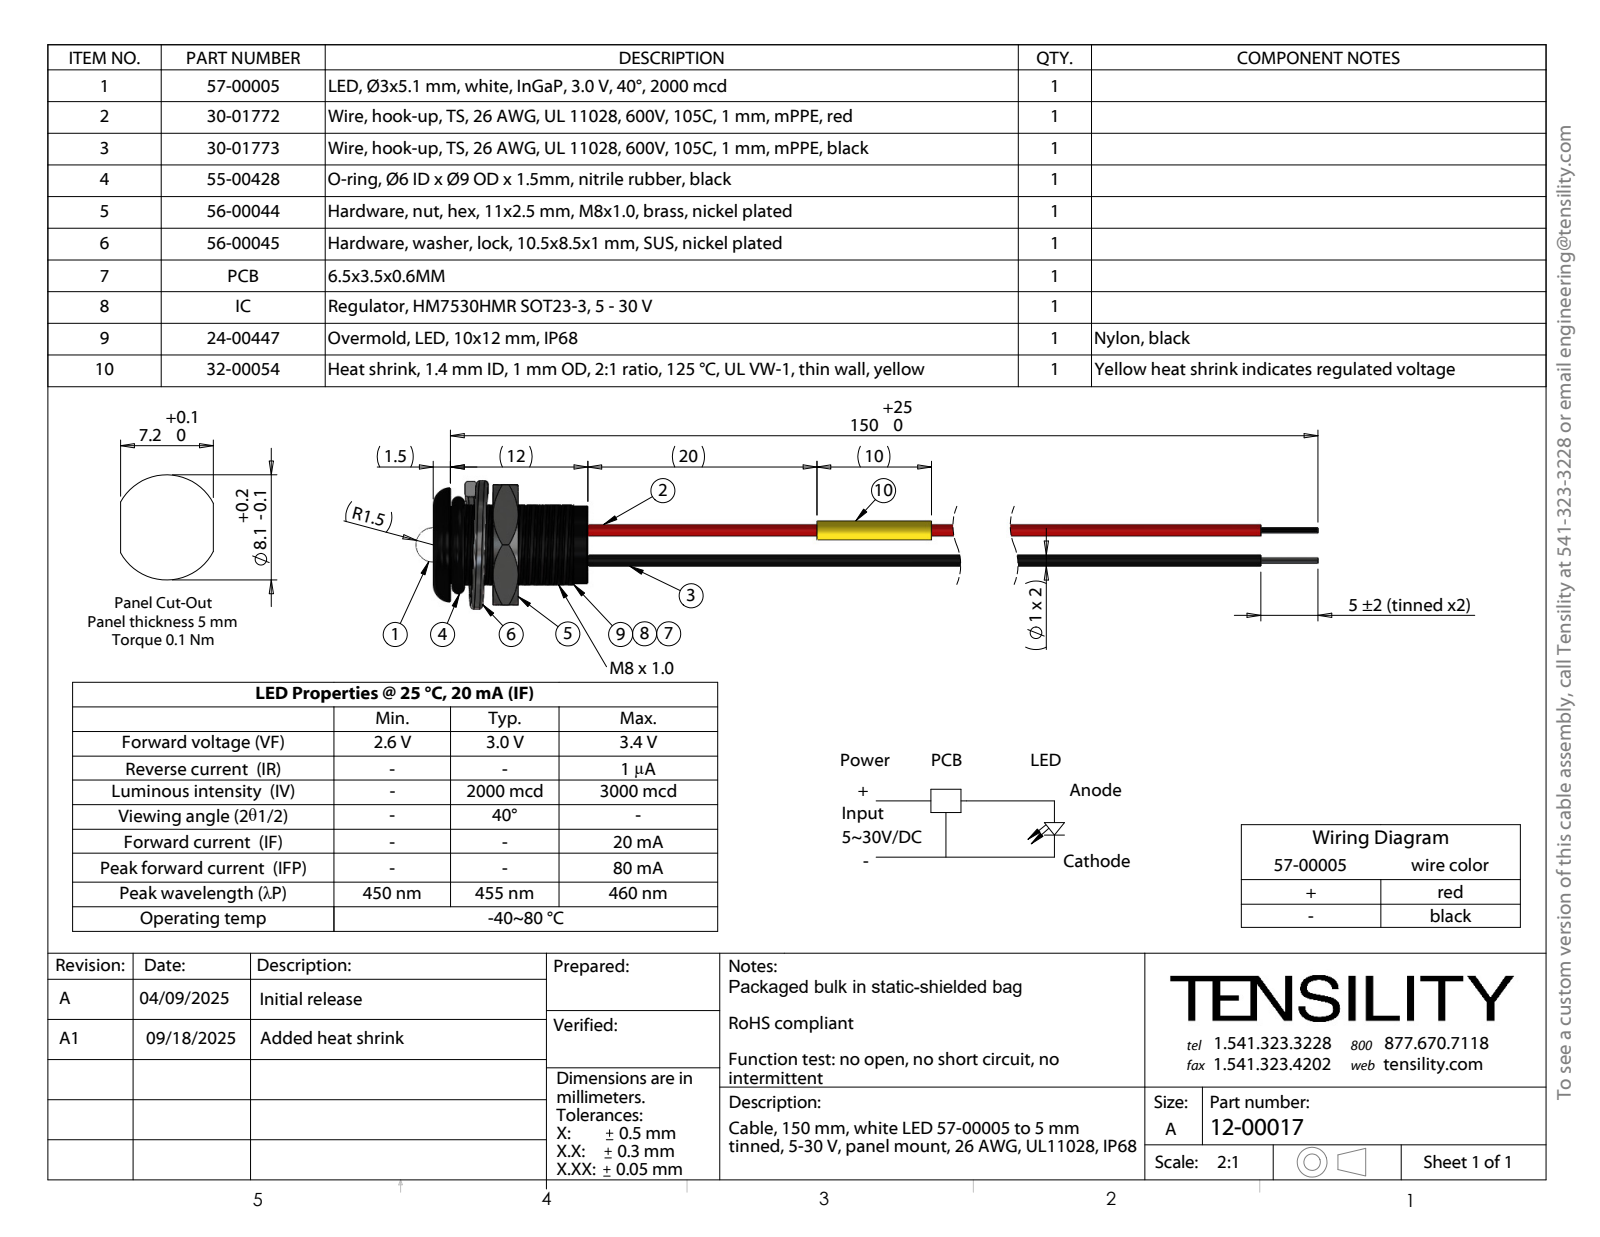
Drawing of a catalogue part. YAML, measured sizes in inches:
part_name: "30-01772_stripped and tinned; 30-01773_stripped and tinned; 56-00045_Split washer; 55-00428 (+4 more)"
step_written_by: "SolidWorks 2021 (CONFIG_CONTROL_DESIGN)"
units: inches
bodies: {solids: 57, faces: 555, planar: 186, cylindrical: 246, other: 123}
overall_size: [6.693, 0.477, 0.441]
volume: 0.061
surface_area: 9.157
round_holes:
  - {diameter: 0.039, count: 2}
round_bosses_or_shafts:
  - {diameter: 0.039, count: 2}
  - {diameter: 0.02, count: 2}
  - {diameter: 0.268, count: 1}
  - {diameter: 0.118, count: 1}
partial_cylinders:
  - {radius: 0.137, count: 1}
  - {radius: 0.157, count: 1}
face_to_face_distances: [0.059, 0.531, 0.472, 0.413, 0.205, 0.146, 0.326, 0.292, 0.233, 0.087]
hole_center_spacings: [0.014, 0.015, 0.013, 0.098, 0.099, 0.096, 0.096, 0.101]
